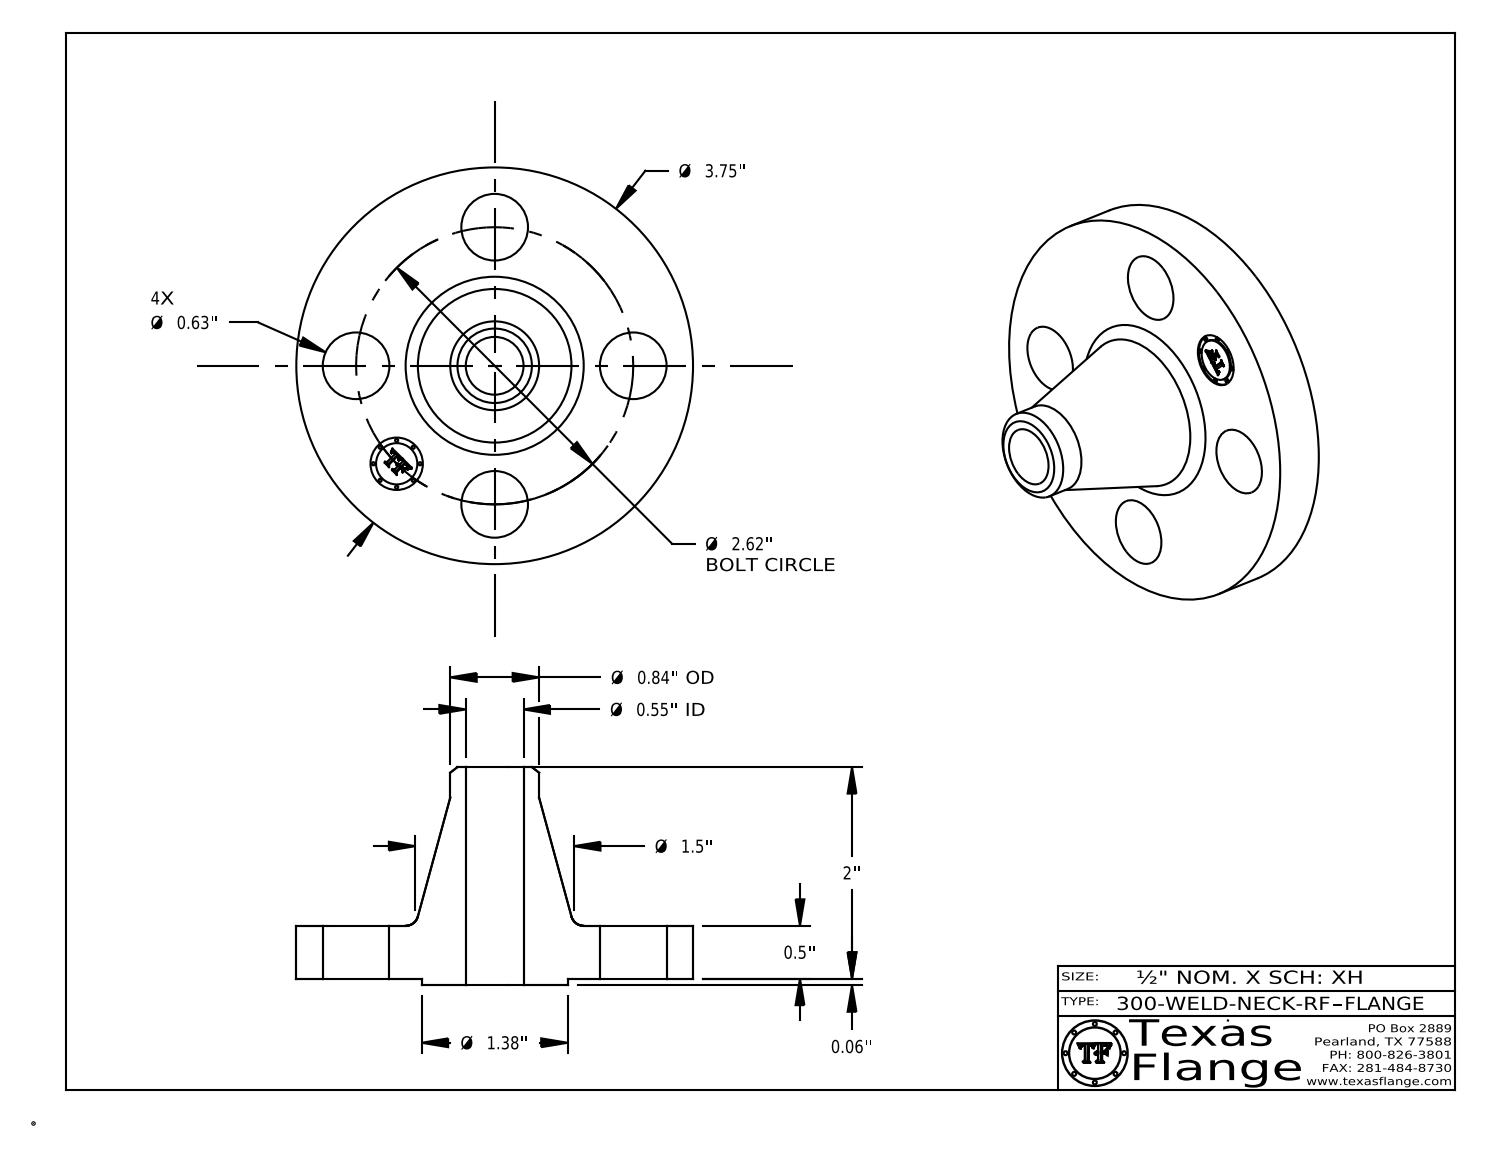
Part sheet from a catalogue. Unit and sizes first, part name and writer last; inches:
Units: inches
Overall size (bounding box): 3.75 × 3.75 × 2.063
Round holes (diameter × count): ⌀0.63 ×4, ⌀0.495 ×1, ⌀0.546 ×1
Round bosses / shafts (diameter × count): ⌀0.03 ×8, ⌀3.75 ×1, ⌀1.38 ×1, ⌀0.84 ×1, ⌀0.39 ×1
Main face-to-face distances: 0.5, 0.063, 0.563, 2.063, 2, 1.5, 0.548, 0.485, 0.015, 1.515
Hole centre spacings: 1.31, 1.852, 1.003, 2.42, 2.62, 1.31
Volume: 6.008 in³ · Surface area: 36.82 in²
Bodies: 1 solid, 411 faces (369 planar, 36 cylindrical, 6 other)
Part name (STEP PRODUCT): 300-WELD-NECK-RF
STEP written by: CATIA V5 STEP AP214 (AUTOMOTIVE_DESIGN)
